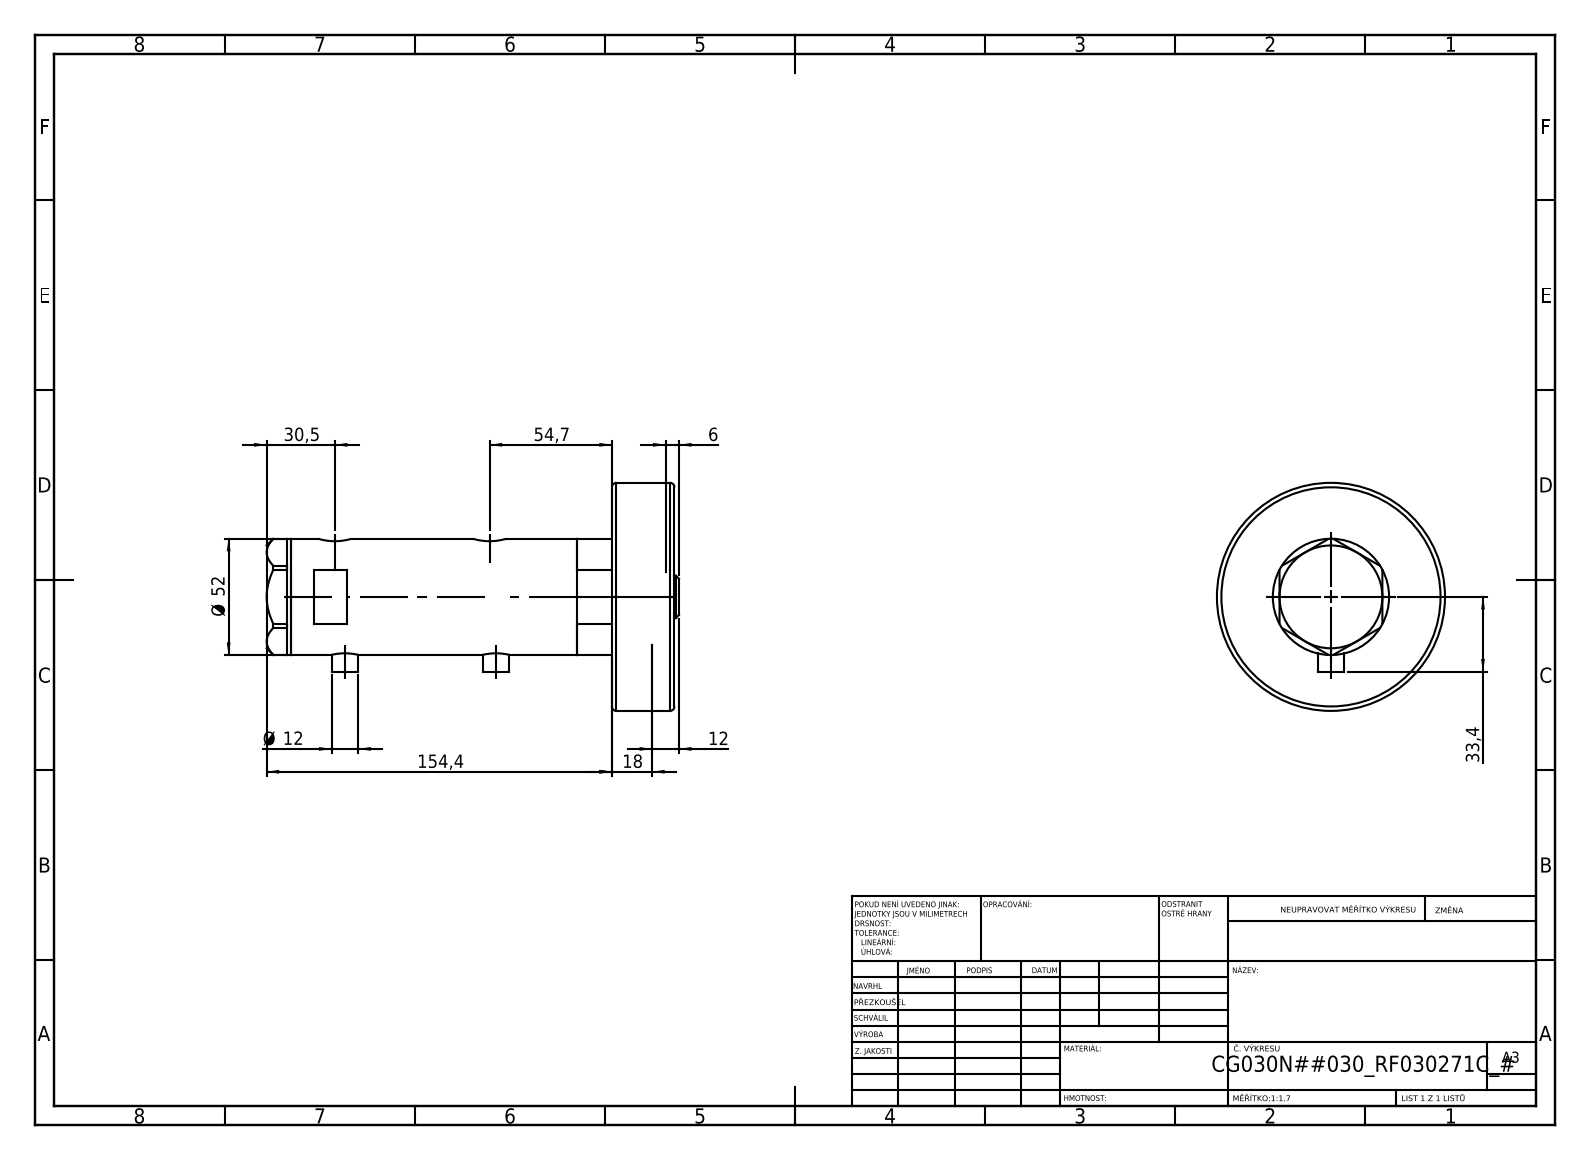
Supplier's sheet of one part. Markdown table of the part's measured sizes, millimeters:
| quantity | value |
| --- | --- |
| part name | V270CG_271C; V270CG_VC; V270CG_BACK; V270CG_MIDDLE (+1 more) |
| STEP written by | SolidWorks 2019 (CONFIG_CONTROL_DESIGN) |
| units | millimeters |
| bodies | 5 solids, 144 faces (67 planar, 53 cylindrical, 24 other) |
| overall size | 184.4 × 102 × 102 |
| volume | 527 985 mm³ |
| surface area | 102 901 mm² |
| round holes (diameter × count) | 9.73 × 2, 12.5 × 2, 15 × 2, 6.5 × 1, 20 × 1, 21.5 × 1, 30 × 1, 33 × 1, 40 × 1, 44 × 1 |
| round bosses / shafts (diameter × count) | 12 × 2, 102 × 1, 52 × 1, 38 × 1, 19 × 1 |
| main face-to-face distances | 28, 143.4, 171.4, 91.5, 51.9, 79.9, 23.8, 67.7, 119.6, 147.6 |
| hole center spacings | 2.9, 4.5, 64.7, 67.6, 69.2, 72.1 |
